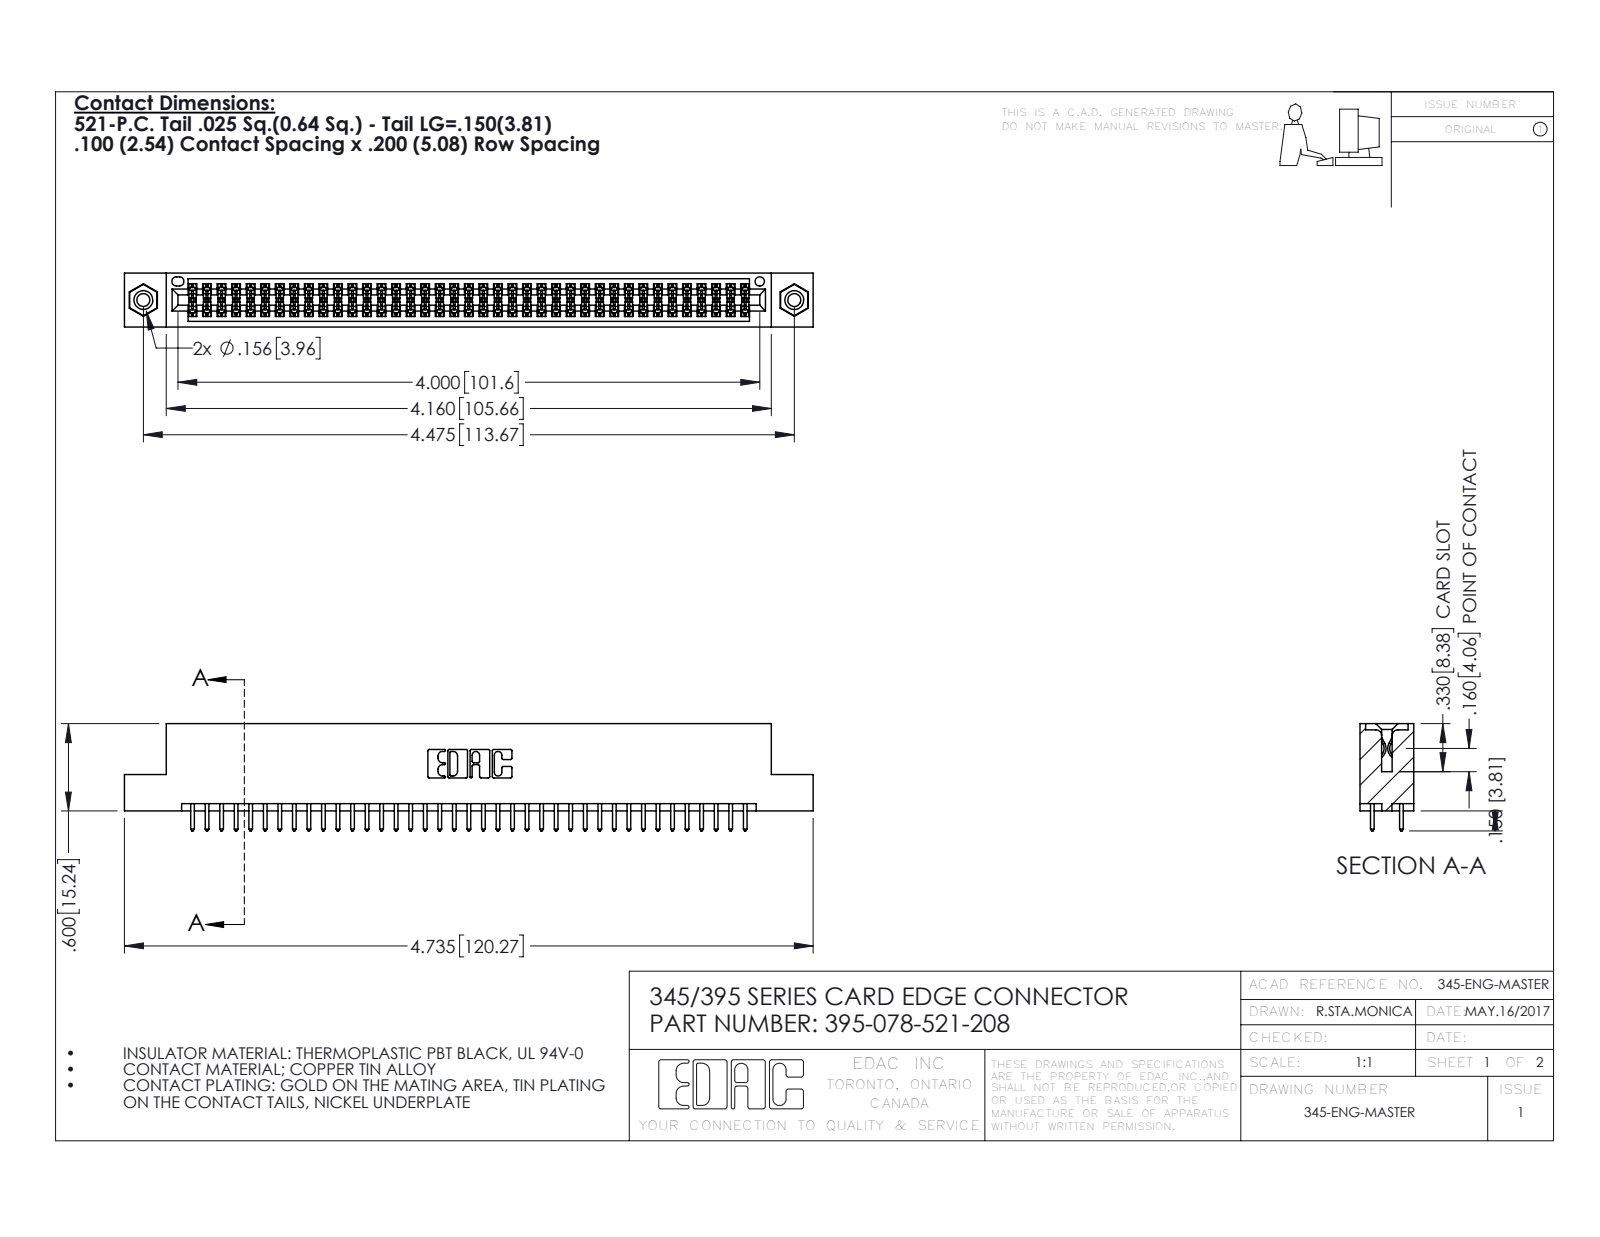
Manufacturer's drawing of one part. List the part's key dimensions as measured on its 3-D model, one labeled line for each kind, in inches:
Part name (STEP PRODUCT): 395-078-521-208; 345 Part_Flush Mounting Lugs - 0.156 Dia-TI; 345-292-001_345-293-121; 345-250-001_345-250-003-102
STEP written by: SolidWorks 2016 (CONFIG_CONTROL_DESIGN)
Units: inches
Bodies: 81 solids, 4086 faces (2686 planar, 1384 cylindrical, 16 other)
Overall size (bounding box): 4.735 × 0.737 × 0.37
Volume: 0.709 in³ · Surface area: 26.23 in²
Round holes (diameter × count): ⌀0.089 ×2, ⌀0.125 ×2, ⌀0.156 ×2, ⌀0.064 ×1
Round bosses / shafts (diameter × count): ⌀0.155 ×2
Partial cylindrical surfaces — rounded edges, fillets, slot ends (radius × count): R0.006 ×117, R0.01 ×78, R0.01 ×22, R0.007 ×6, R0.031 ×6, R0.026 ×3, R0.014 ×2, R0.019 ×2
Main face-to-face distances: 0.072, 0.298, 0.2, 0.37, 0.098, 0.272, 0.025, 0.225, 0.175, 0.149
Hole centre spacings: 0.27, 4.239, 4.475
